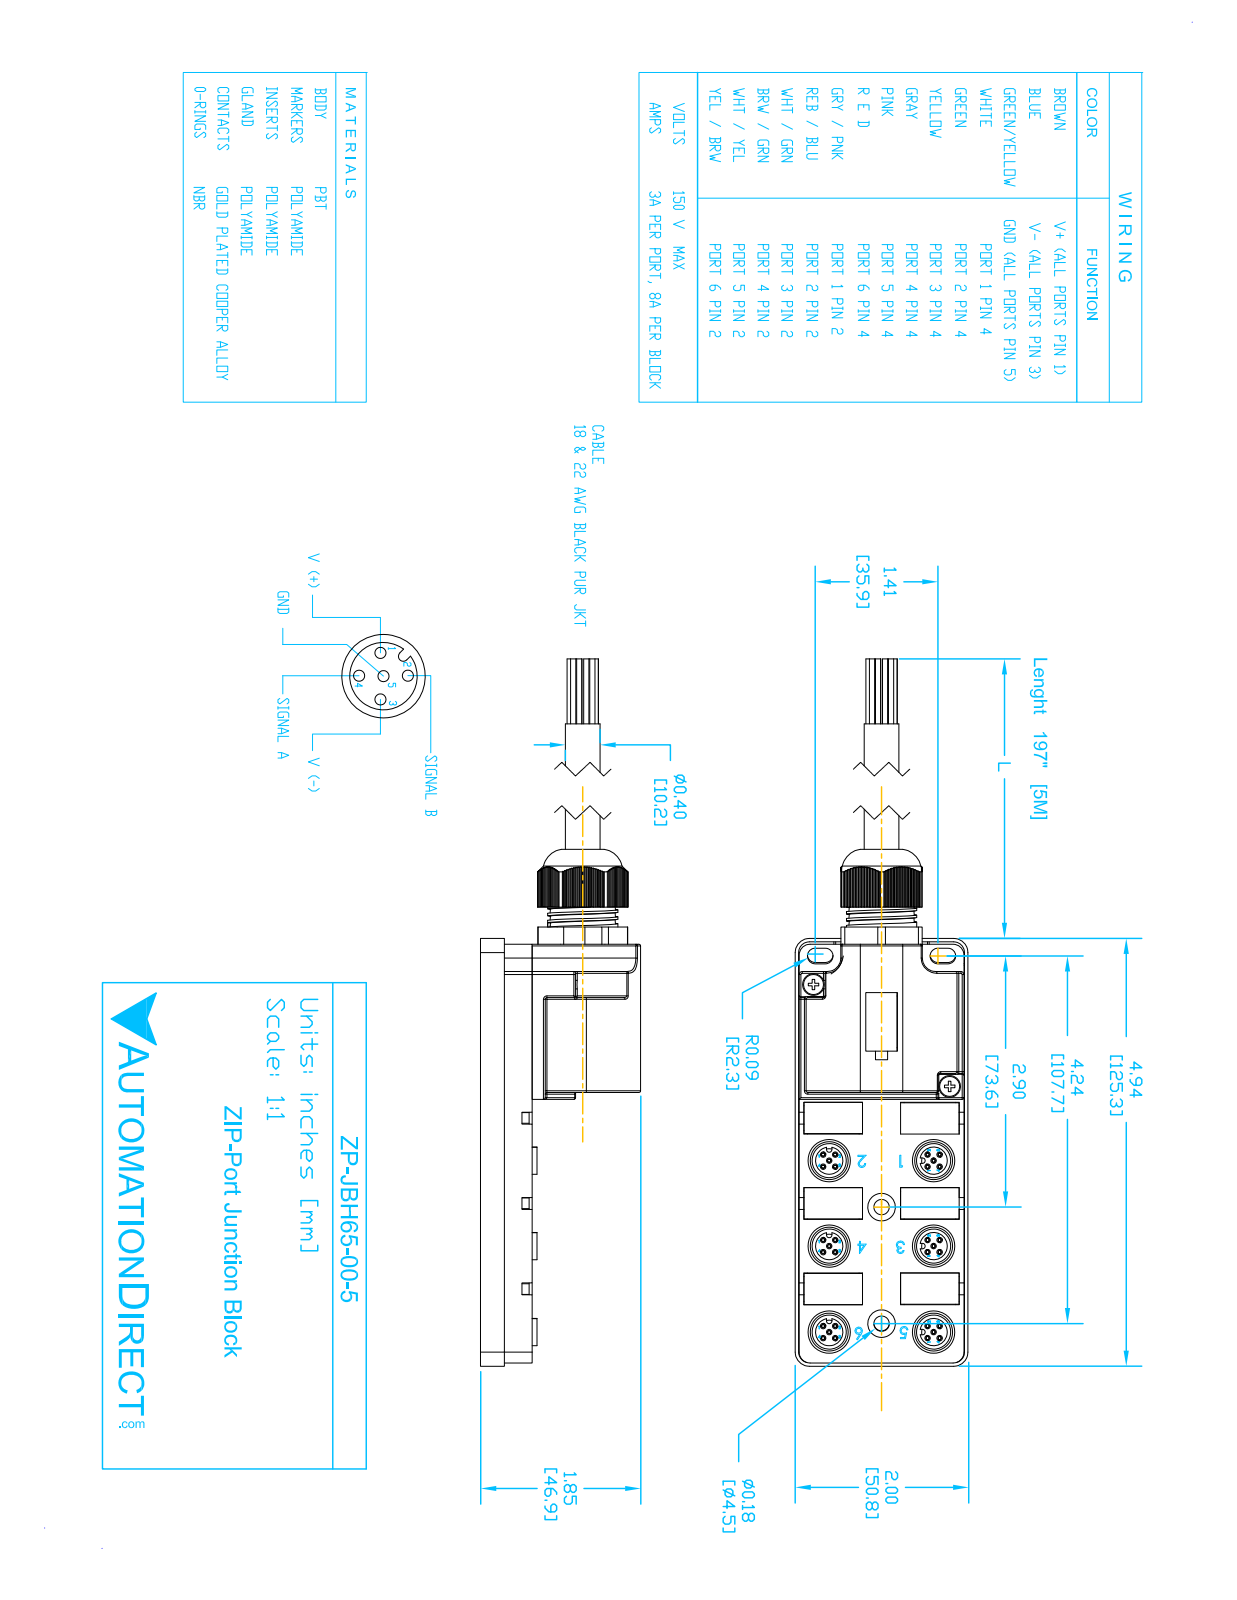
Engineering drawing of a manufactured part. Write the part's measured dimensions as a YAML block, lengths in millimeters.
part_name: "ZP-JBH64-00-ZZ"
step_written_by: "SolidWorks 2016 (AUTOMOTIVE_DESIGN)"
units: millimeters
bodies: {solids: 8, faces: 1405, planar: 800, cylindrical: 390, other: 215}
overall_size: [199.85, 50.57, 46.89]
volume: 149063
surface_area: 40181
round_holes:
  - {diameter: 1.09, count: 30}
  - {diameter: 1.6, count: 30}
  - {diameter: 2.36, count: 8}
  - {diameter: 11.1, count: 6}
  - {diameter: 12.4, count: 6}
  - {diameter: 4.5, count: 2}
  - {diameter: 6.35, count: 2}
  - {diameter: 6.6, count: 2}
  - {diameter: 8.08, count: 2}
  - {diameter: 1.27, count: 1}
  - {diameter: 9.4, count: 1}
  - {diameter: 12.45, count: 1}
round_bosses_or_shafts:
  - {diameter: 4.83, count: 7}
  - {diameter: 15.8, count: 4}
  - {diameter: 8, count: 4}
  - {diameter: 8, count: 2}
  - {diameter: 5.84, count: 2}
  - {diameter: 20.57, count: 1}
  - {diameter: 9.53, count: 1}
  - {diameter: 9.52, count: 1}
partial_cylinders:
  - {radius: 0.51, count: 34}
  - {radius: 2.29, count: 8}
  - {radius: 0.8, count: 6}
  - {radius: 1.18, count: 4}
  - {radius: 4.17, count: 4}
  - {radius: 0.89, count: 2}
  - {radius: 3.2, count: 2}
  - {radius: 3.97, count: 2}
face_to_face_distances: [15.14, 7, 8.14, 8.99, 1.99, 6.15, 48.26, 0.89, 7.94, 14.94]
hole_center_spacings: [2.5, 3.53, 28.84, 3.54, 23.37, 25.07, 30.56, 32.38]
